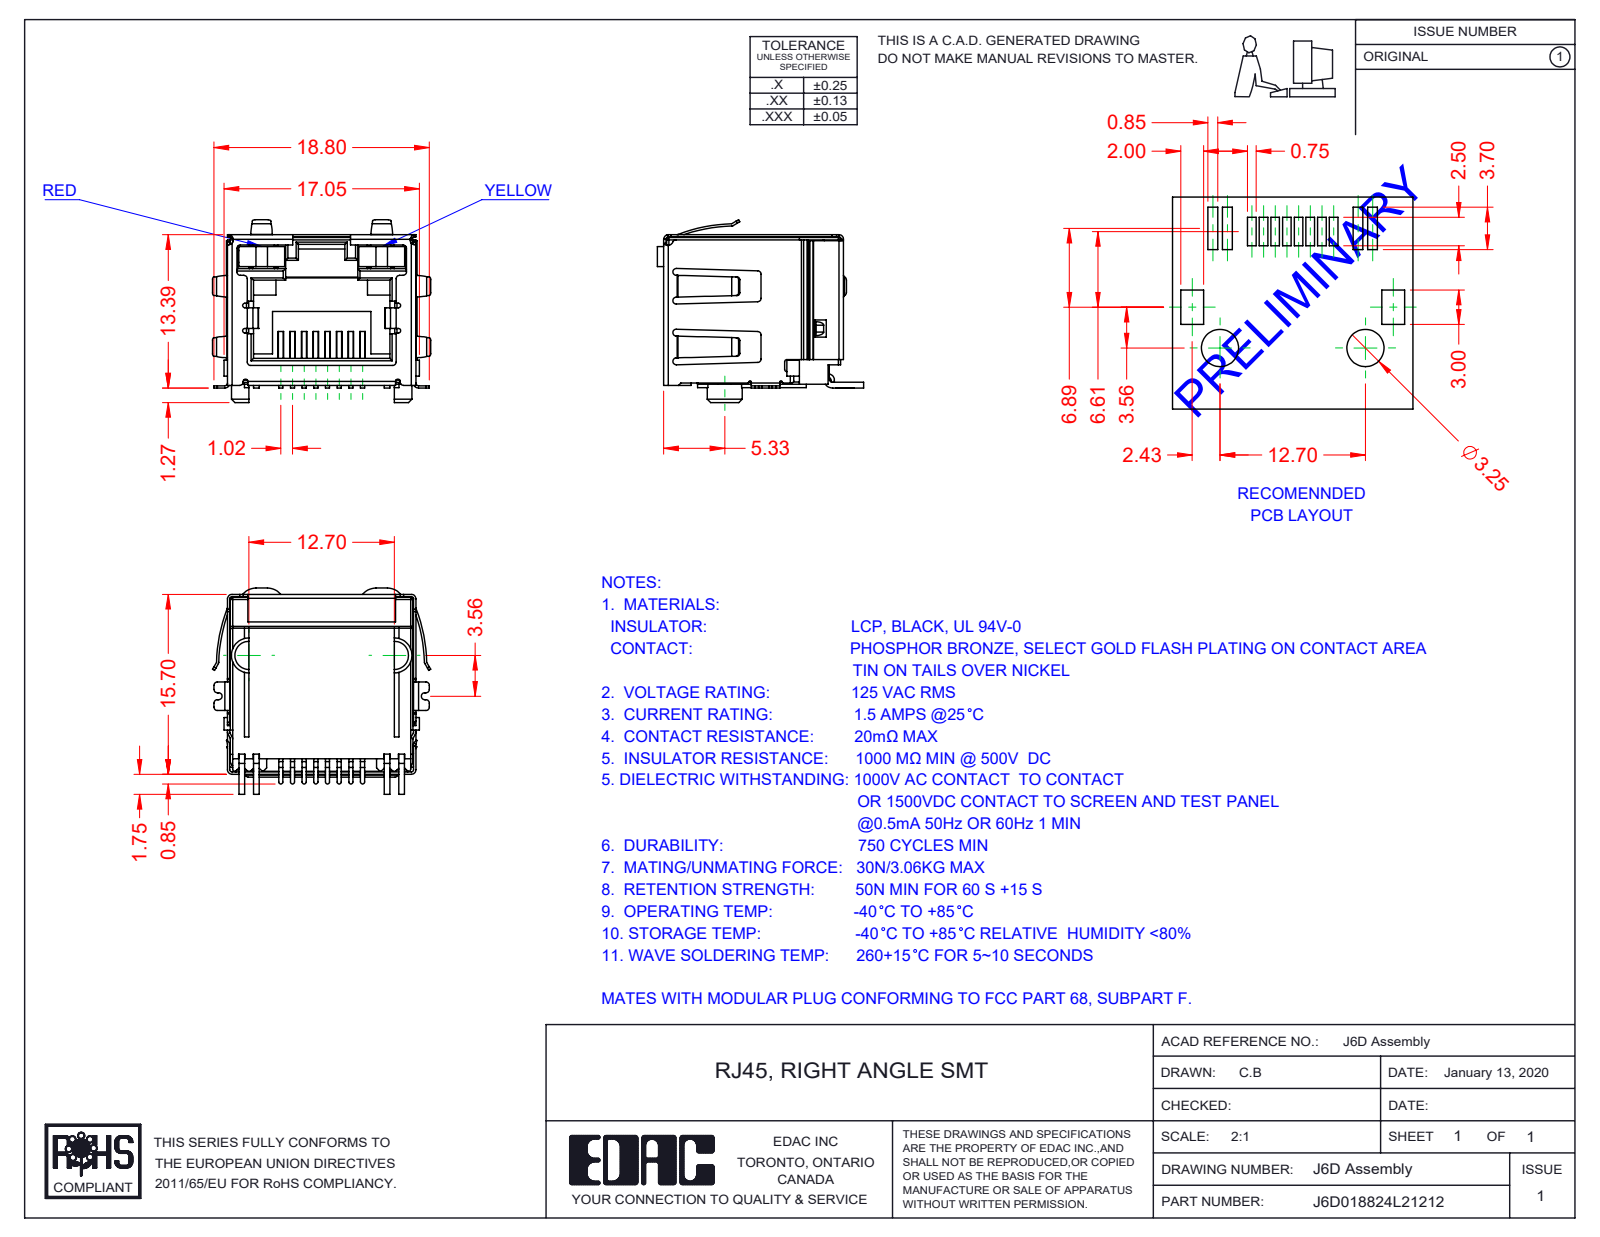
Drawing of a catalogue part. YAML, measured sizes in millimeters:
part_name: "6D Insulator; J6D018824L21212; 6D LED LH_2-Red; 6D Contacts (+2 more)"
step_written_by: "SolidWorks 2016 (CONFIG_CONTROL_DESIGN)"
units: millimeters
bodies: {solids: 12, faces: 1028, planar: 701, cylindrical: 282, other: 45}
overall_size: [19.06, 18, 15.95]
volume: 1790
surface_area: 4796
partial_cylinders:
  - {radius: 0.3, count: 55}
  - {radius: 0.2, count: 40}
  - {radius: 0.4, count: 19}
  - {radius: 0.25, count: 16}
  - {radius: 0.1, count: 12}
  - {radius: 0.15, count: 8}
  - {radius: 0.18, count: 8}
  - {radius: 0.5, count: 6}
face_to_face_distances: [16, 16.2, 16.25, 2.25, 1, 15.95, 12.8, 0.45, 13.05, 10.6]
